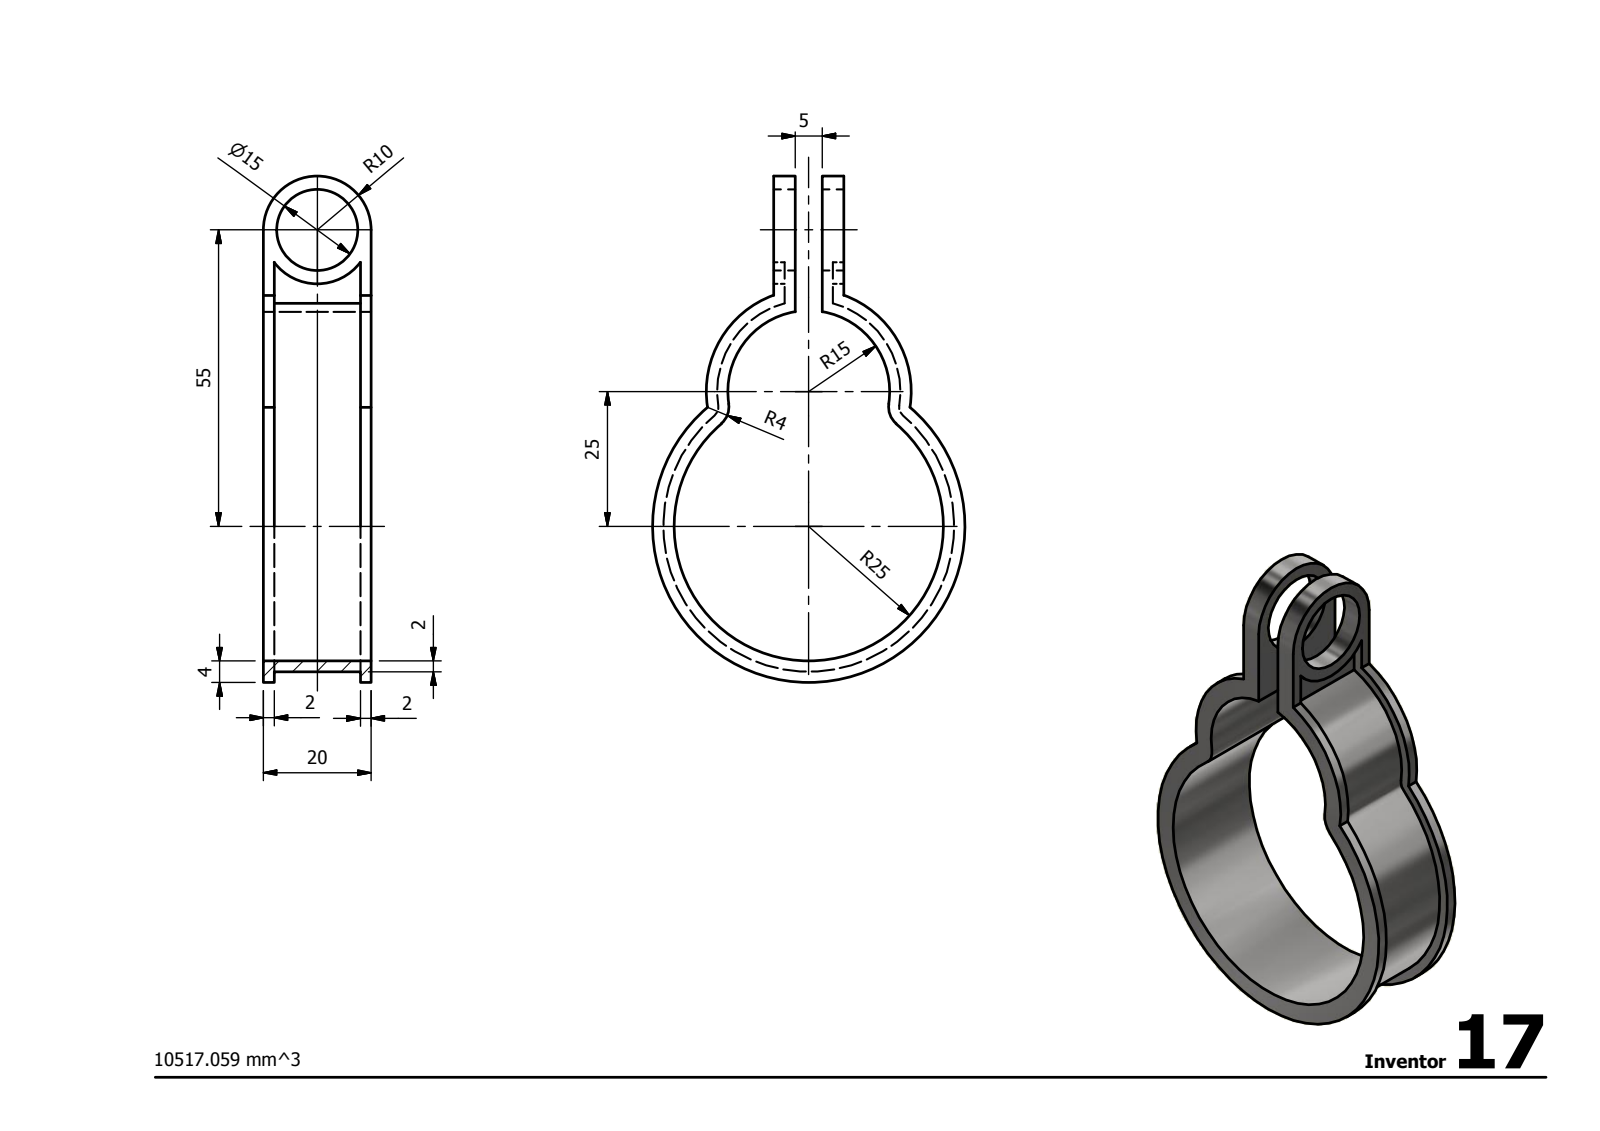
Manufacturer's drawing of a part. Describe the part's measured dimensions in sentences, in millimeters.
Its 3-D file was written by "Autodesk Inventor 2014 (AUTOMOTIVE_DESIGN)". It is 1 solid with 32 faces: 10 planar, 22 cylindrical and 0 other. Overall it measures 94 by 58 by 20 millimeters. Its volume is 10 517 cubic millimeters and its surface area 11 549 square millimeters. Round holes: 1 of diameter 15. Round bosses or shafts: 1 of diameter 20. Partial cylindrical surfaces (rounded edges, fillets, slot ends): 2 of radius 2, 2 of radius 4, 1 of radius 15, 1 of radius 17, 1 of radius 19, 1 of radius 25, 1 of radius 27, 1 of radius 29. The main face-to-face distances are 2, 20, 18, 9, 16, 4, 5, 13, 11, 7.
